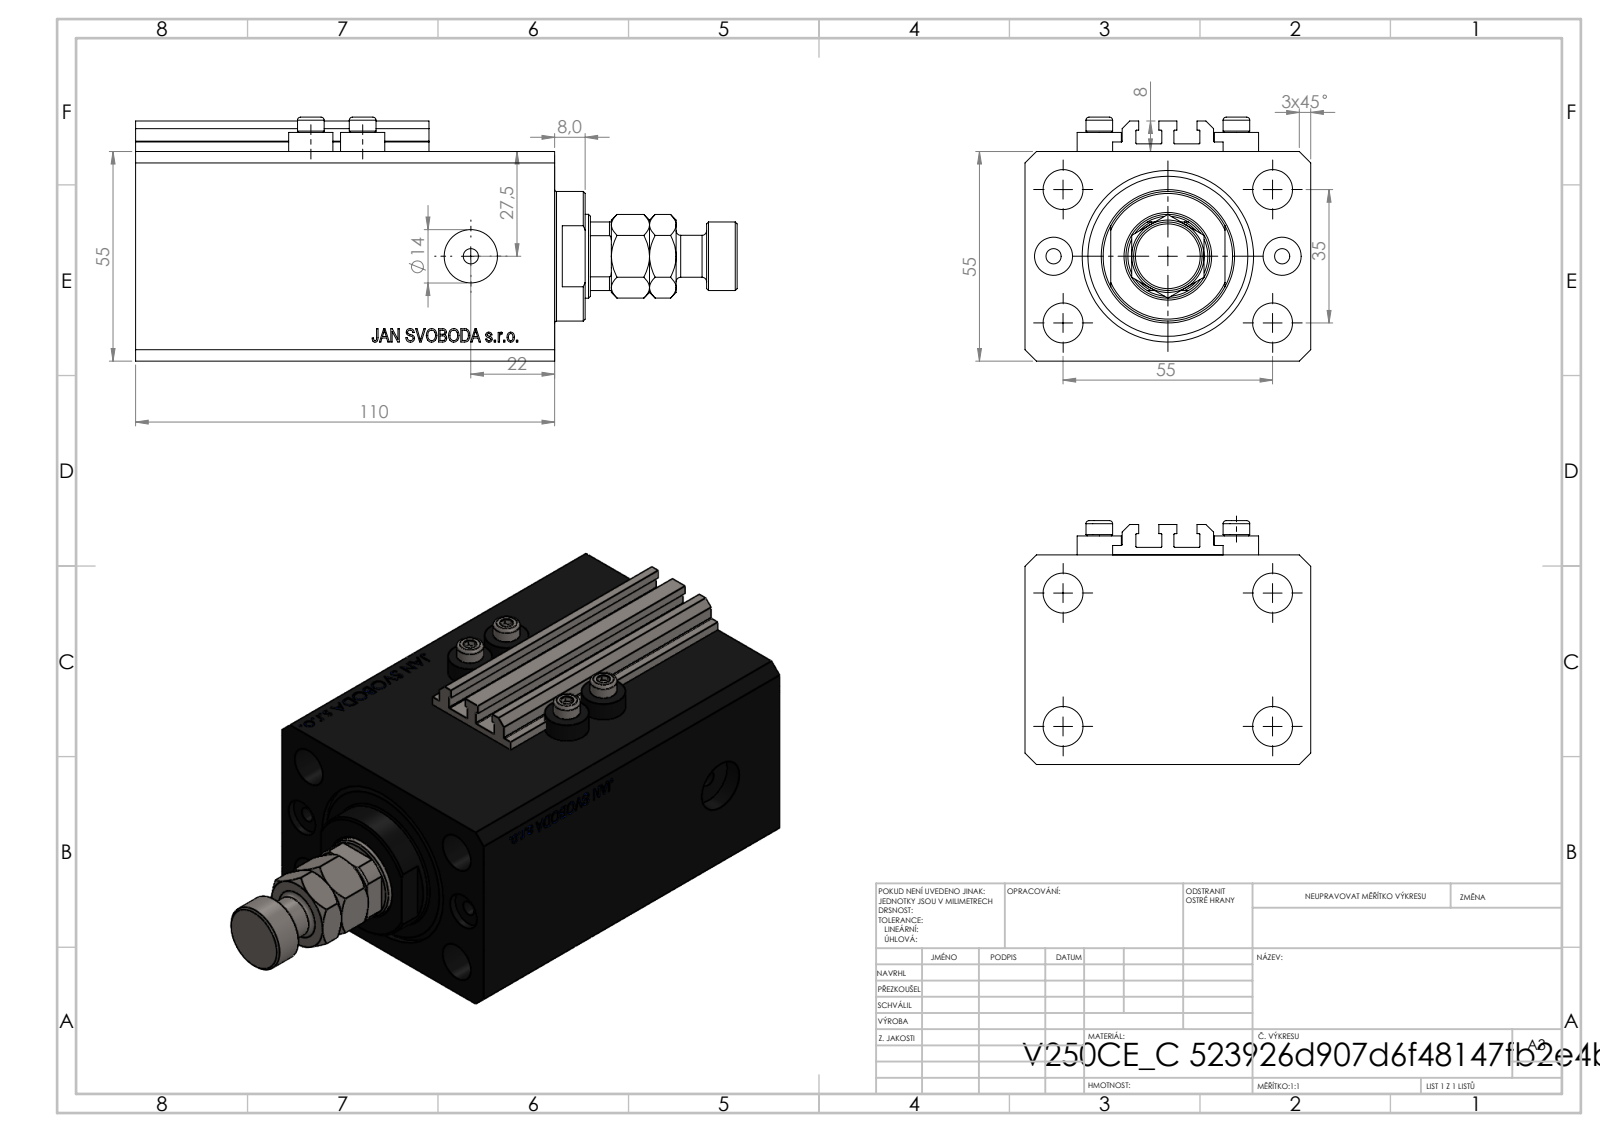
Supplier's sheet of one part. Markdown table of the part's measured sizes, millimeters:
| quantity | value |
| --- | --- |
| part name | V250CE_C_Body; MFA; V250CE_VC_C; ALLEN BOLT V250CE (+1 more) |
| STEP written by | SolidWorks 2019 (CONFIG_CONTROL_DESIGN) |
| units | millimeters |
| bodies | 9 solids, 1085 faces (519 planar, 90 cylindrical, 476 other) |
| overall size | 157.9 × 75 × 64 |
| volume | 416 936 mm³ |
| surface area | 96 470 mm² |
| round holes (diameter × count) | 4 × 8, 10.5 × 5, 10 × 2, 14 × 2, 22 × 1, 32 × 1, 45 × 1 |
| round bosses / shafts (diameter × count) | 11.6 × 4, 7 × 4, 34 × 1, 18 × 1, 11 × 1 |
| partial cylindrical surfaces (radius × count) | 0.2 × 10, 10.5 × 1 |
| main face-to-face distances | 55, 75, 110, 82.9, 27.1, 9.9, 73, 100.1, 2.5, 8 |
| hole center spacings | 17.68, 32.6, 60.1, 13.6, 30, 35, 36, 38.48 |
